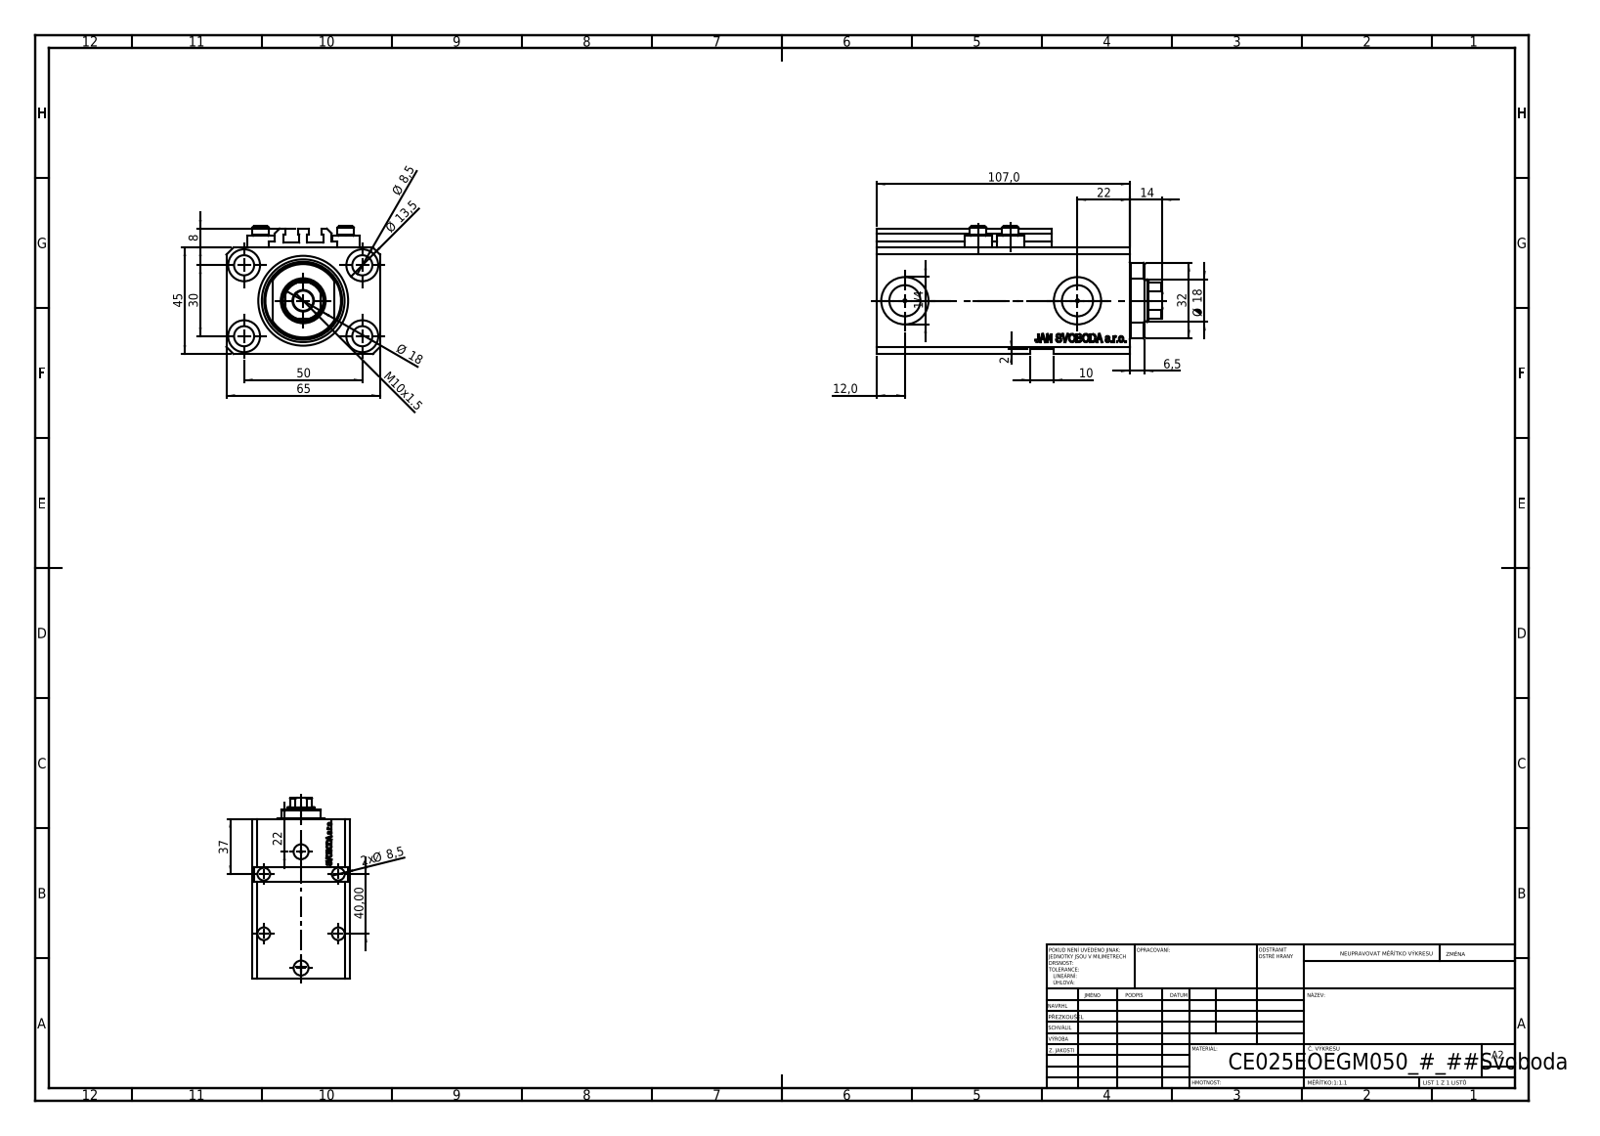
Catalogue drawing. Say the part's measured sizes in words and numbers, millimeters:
The part is named "ALLEN BOLT V250CE; V250CE_E_Body; V250CE_VC_E; V250CE_C_VCP". Its 3-D file was written by "SolidWorks 2019 (CONFIG_CONTROL_DESIGN)". It is 8 solids with 1087 faces: 511 planar, 146 cylindrical and 430 other. Overall it measures 121 by 65 by 54 millimeters. Its volume is 273 399 cubic millimeters and its surface area 76 876 square millimeters. Round holes: 9 of diameter 8.5, 4 of diameter 1.25, 4 of diameter 4, 4 of diameter 13.5, 2 of diameter 10, 2 of diameter 13.16, 2 of diameter 20, 1 of diameter 18, 1 of diameter 25, 1 of diameter 38. Round bosses or shafts: 4 of diameter 11.6, 4 of diameter 7. Partial cylindrical surfaces (rounded edges, fillets, slot ends): 10 of radius 0.2, 1 of radius 8.5, 1 of radius 16. The main face-to-face distances are 45, 65, 93, 2, 14, 47, 107, 2.5, 10, 20.5. The hole center spacings are 29.15, 50, 13.6, 14.76, 15.12, 27.51, 27.89, 30.
